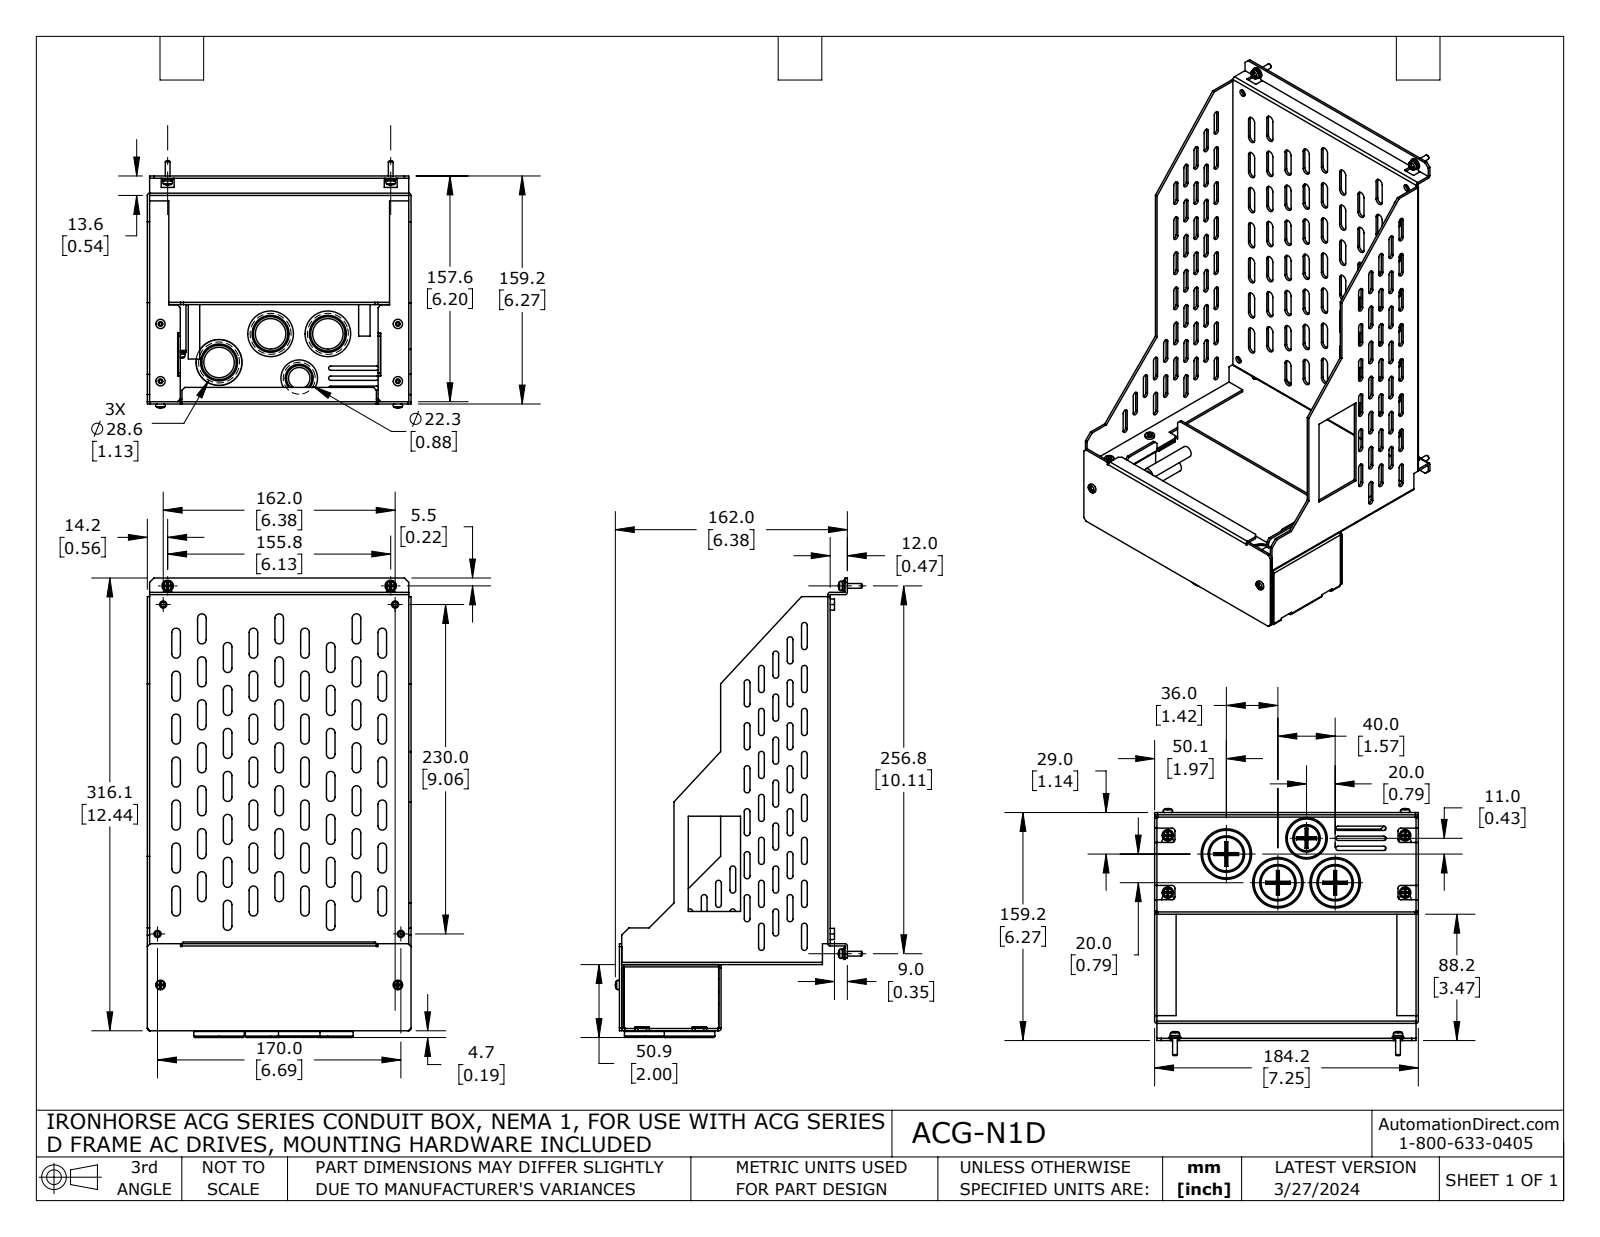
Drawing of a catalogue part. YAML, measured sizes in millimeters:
part_name: "ACG-N1D"
step_written_by: "SolidWorks 2021 (AUTOMOTIVE_DESIGN)"
units: millimeters
bodies: {solids: 18, faces: 1658, planar: 824, cylindrical: 695, other: 139}
overall_size: [320.8, 184.2, 172.5]
volume: 230600
surface_area: 300300
round_holes:
  - {diameter: 3.3, count: 10}
  - {diameter: 5, count: 4}
  - {diameter: 8.5, count: 4}
  - {diameter: 4, count: 3}
  - {diameter: 23.5, count: 3}
  - {diameter: 28.6, count: 3}
  - {diameter: 32.3, count: 3}
  - {diameter: 4.3, count: 2}
  - {diameter: 17.2, count: 1}
  - {diameter: 22.3, count: 1}
  - {diameter: 26, count: 1}
round_bosses_or_shafts:
  - {diameter: 8, count: 11}
  - {diameter: 6.6, count: 9}
  - {diameter: 6.5, count: 6}
  - {diameter: 3.3, count: 5}
  - {diameter: 35.3, count: 3}
  - {diameter: 31.9, count: 3}
  - {diameter: 27.9, count: 3}
  - {diameter: 29, count: 1}
partial_cylinders:
  - {radius: 3, count: 126}
  - {radius: 2, count: 92}
  - {radius: 0.5, count: 28}
  - {radius: 1.6, count: 17}
  - {radius: 1.5, count: 6}
  - {radius: 2.3, count: 4}
  - {radius: 2.5, count: 4}
  - {radius: 5, count: 3}
face_to_face_distances: [1.6, 182.6, 145.6, 76.2, 69.4, 184.2, 181, 144, 67.8, 46.2]
hole_center_spacings: [40, 165.8, 5, 165.9, 170.6, 24.7, 35, 35.7]
